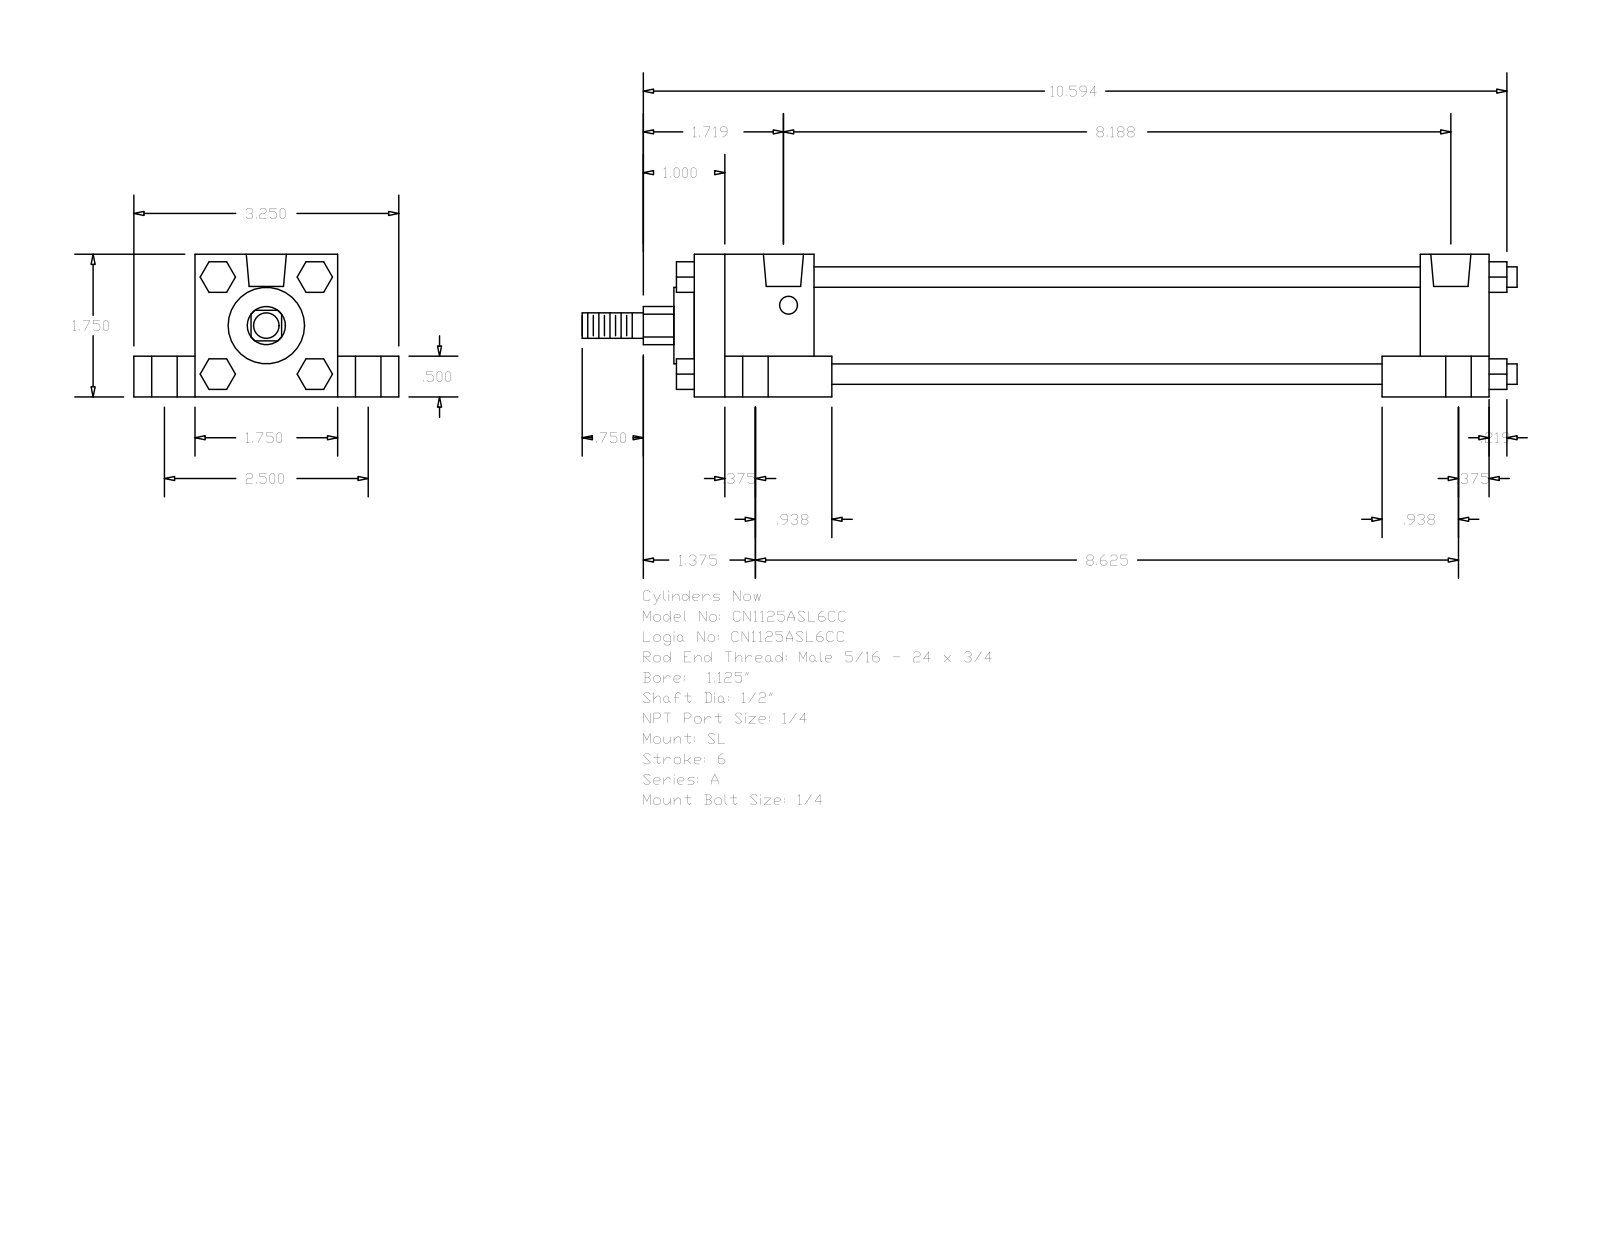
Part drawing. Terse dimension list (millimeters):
name: A_SL__0112_0.5
written by: GSSL Pune (CONFIG_CONTROL_DESIGN)
unit: mm
bodies: 0 solids, 150 faces (114 planar, 36 cylindrical, 0 other)
size: 291.31 × 82.55 × 44.45
holes: 4× ⌀5.56, 4× ⌀7.94, 4× ⌀14.29, 2× ⌀12.49
bosses: 4× ⌀6.35, 1× ⌀31.88, 1× ⌀23.81, 1× ⌀12.7, 1× ⌀7.94
rounds: 1× R5.94
face distances: 44.46, 31.76, 12.7, 19.04, 63.5, 210.34, 247.64, 226.21, 21.43, 37.3
hole spacings: 31.84, 32, 32.93, 33.39, 63.5, 204.79, 211.16, 212.72
